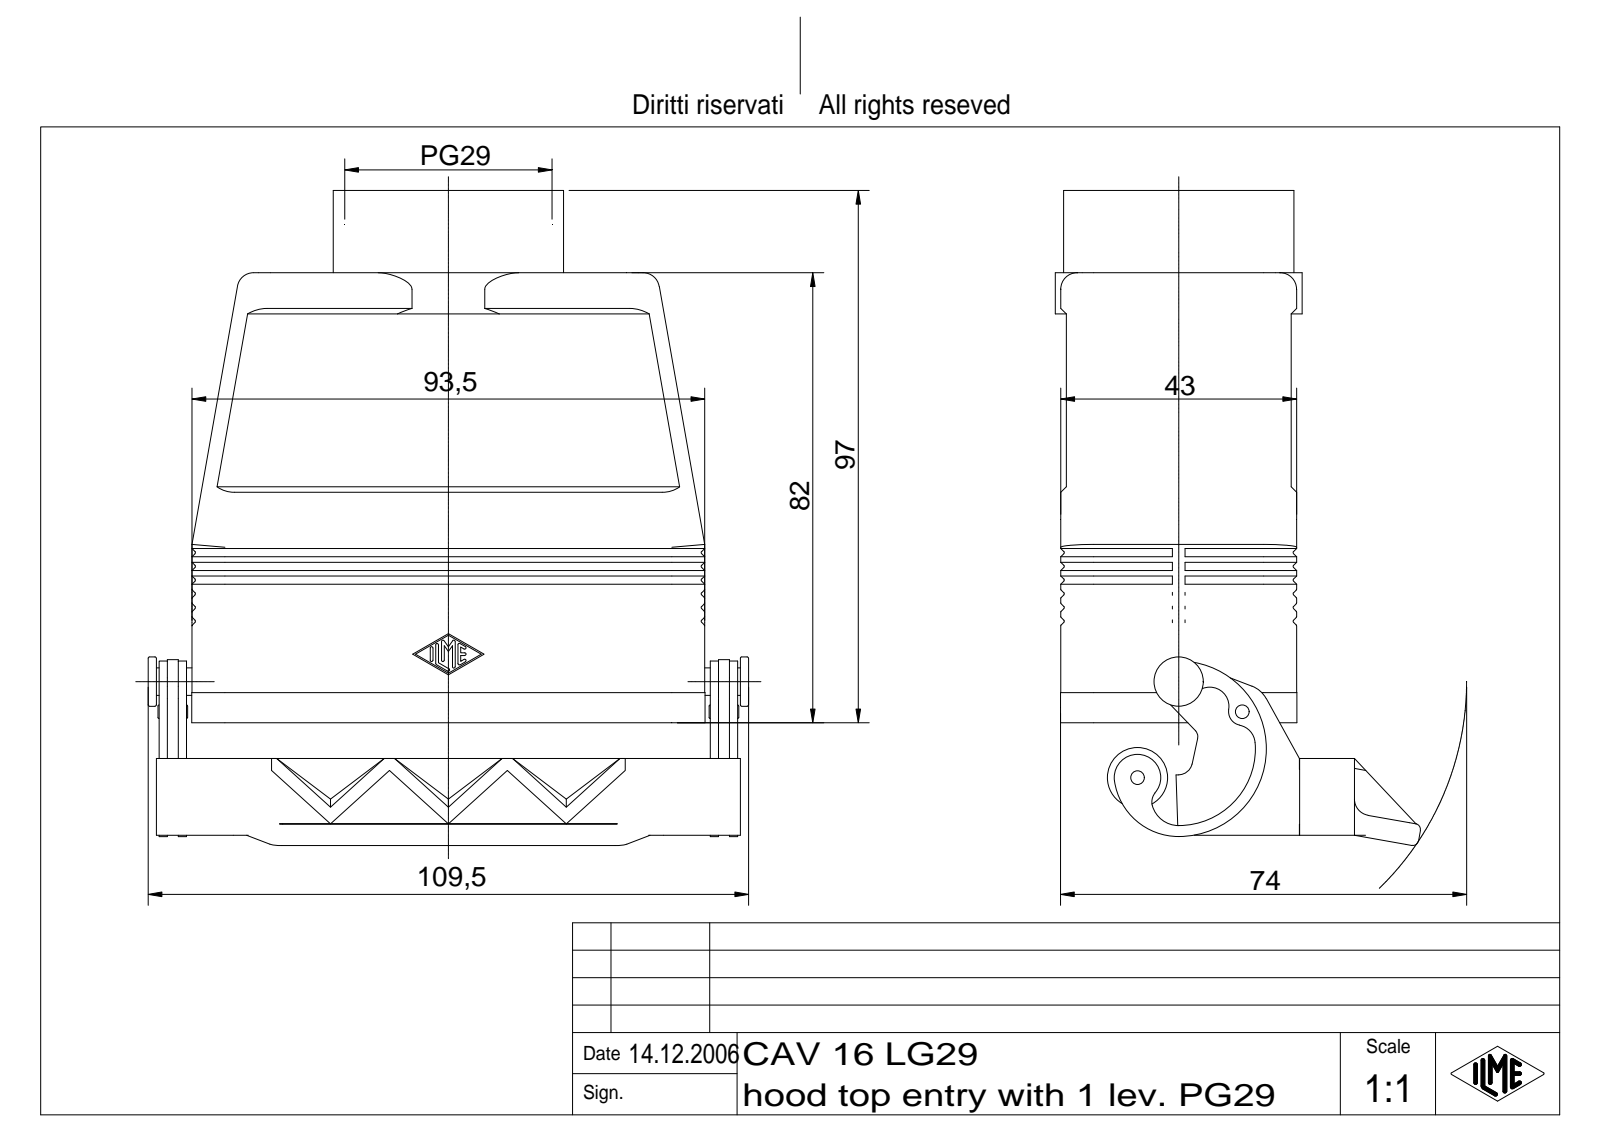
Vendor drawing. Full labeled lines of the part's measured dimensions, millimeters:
Part name (STEP PRODUCT): CAV 16 LG29
STEP written by: Autodesk Inventor 7 (AUTOMOTIVE_DESIGN)
Units: millimetres
Bodies: 1 solid, 947 faces (222 planar, 324 cylindrical, 401 other)
Overall size (bounding box): 119.37 × 109.5 × 66.59
Volume: 104 816 mm³ · Surface area: 61 733 mm²
Round holes (diameter × count): ⌀2.5 ×1, ⌀33.48 ×1, ⌀35.48 ×1
Round bosses / shafts (diameter × count): ⌀45 ×1, ⌀42 ×1, ⌀11 ×1, ⌀9 ×1, ⌀5 ×1, ⌀3.1 ×1, ⌀2 ×1
Partial cylindrical surfaces — rounded edges, fillets, slot ends (radius × count): R0.2 ×52, R0.25 ×32, R2.5 ×9, R6 ×8, R3 ×7, R1 ×6, R2.45 ×4, R6.05 ×4
Main face-to-face distances: 3.45, 3.5, 39.55, 39.5, 36.05, 36.1, 36, 2.45, 1, 38.55
